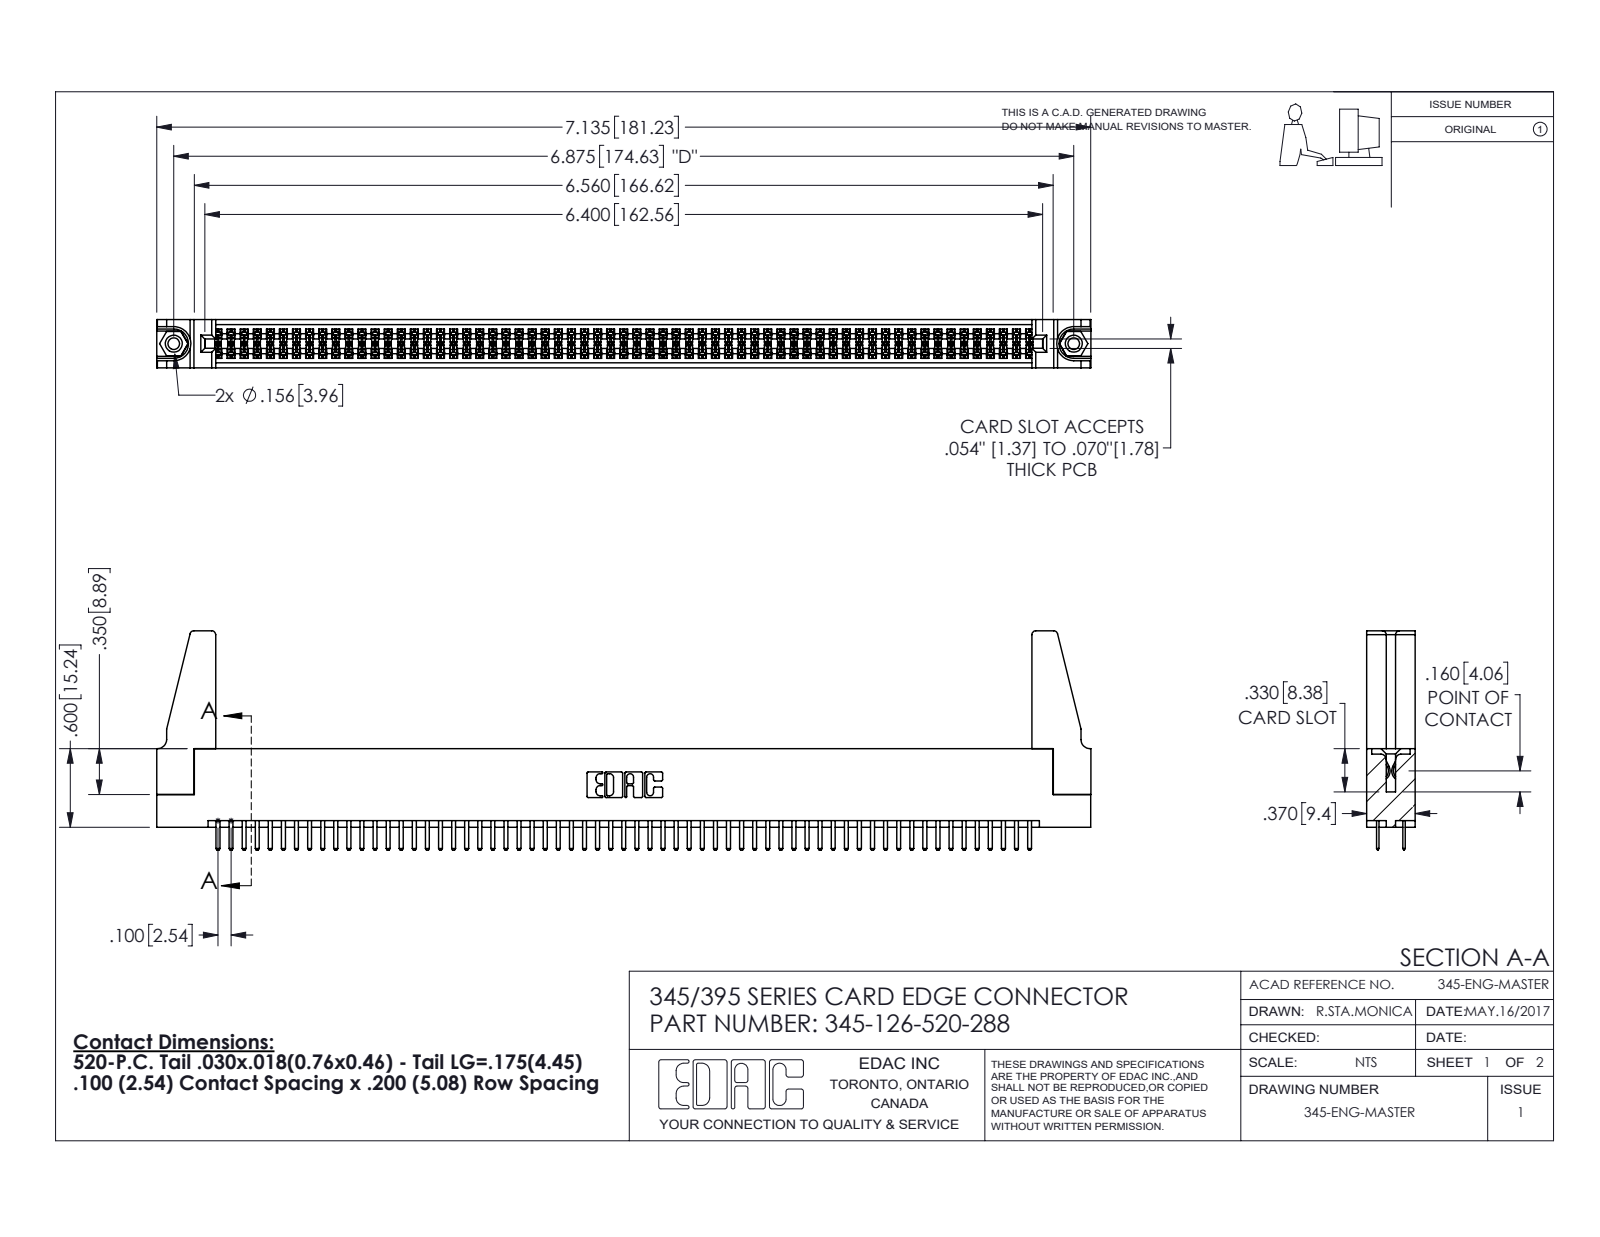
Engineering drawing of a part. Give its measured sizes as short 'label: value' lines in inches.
name: 345-292-001_345-293-120; 345-126-520-288; 345-220-078_345-220-088; 345 Part_Flush Mounting Lugs - 0.156 Dia-TH (+1 more)
written by: SolidWorks 2016 (CONFIG_CONTROL_DESIGN)
unit: in
bodies: 131 solids, 7054 faces (4562 planar, 2476 cylindrical, 16 other)
size: 7.136 × 1.675 × 0.37
volume: 1.281 in³; area: 45.95 in²
holes: 2× ⌀0.089, 2× ⌀0.125, 2× ⌀0.156, 1× ⌀0.064
bosses: 2× ⌀0.155
rounds: 189× R0.006, 130× R0.01, 22× R0.01, 8× R0.03, 6× R0.007, 6× R0.031, 3× R0.026, 2× R0.014
face distances: 0.072, 0.298, 0.37, 0.2, 0.098, 0.272, 0.025, 0.225, 0.022, 0.072
hole spacings: 0.27, 6.639, 6.875
